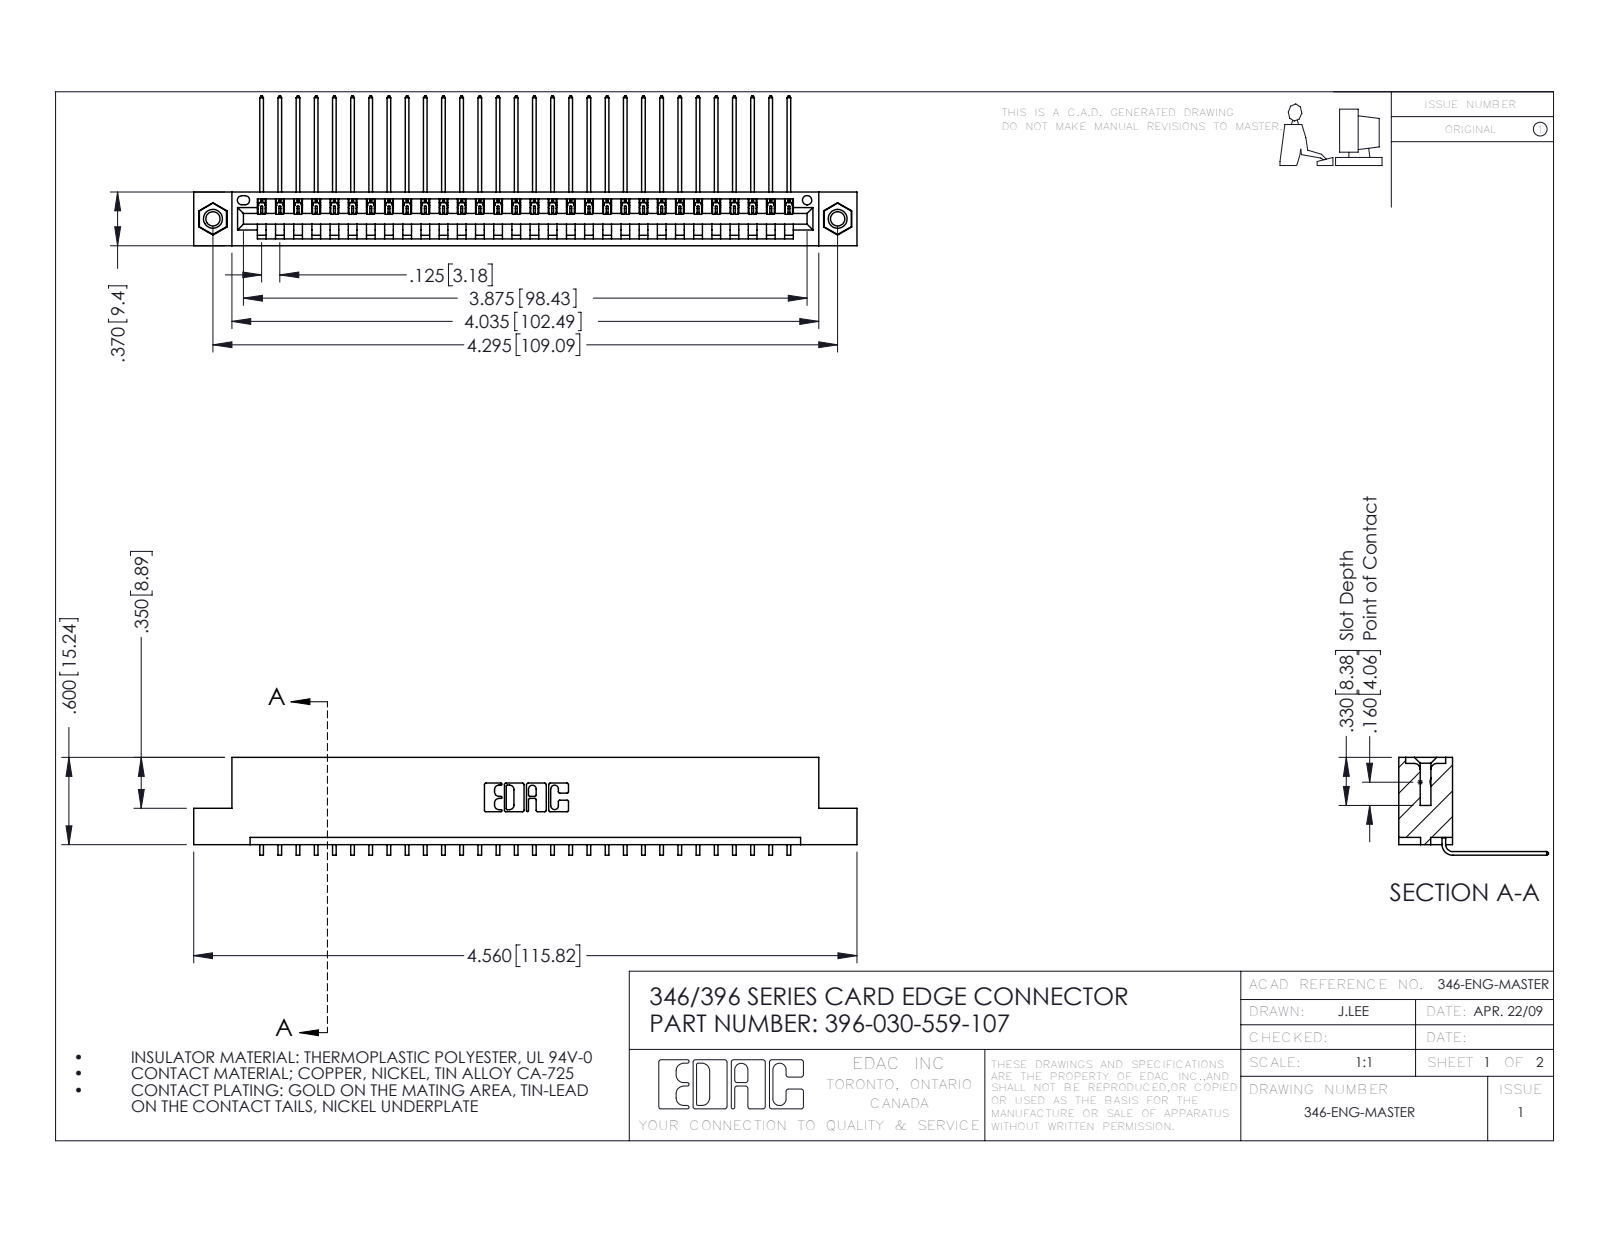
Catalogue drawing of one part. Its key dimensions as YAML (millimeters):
part_name: "396-030-559-107; 346 Part_Flush Mounting Lugs - 0.156 Dia-TI; 345-250-001_345-250-005-103; 345-292-001_558 559 Tail - 1"
step_written_by: "SolidWorks 2016 (CONFIG_CONTROL_DESIGN)"
units: millimeters
bodies: {solids: 33, faces: 1982, planar: 1368, cylindrical: 598, other: 16}
overall_size: [115.8, 26.2, 17.1]
volume: 11100
surface_area: 14360
round_holes:
  - {diameter: 2.5, count: 2}
  - {diameter: 3.2, count: 2}
  - {diameter: 4, count: 2}
  - {diameter: 1.6, count: 1}
round_bosses_or_shafts:
  - {diameter: 3.9, count: 2}
partial_cylinders:
  - {radius: 0.2, count: 60}
  - {radius: 0.3, count: 22}
  - {radius: 0.2, count: 6}
  - {radius: 0.8, count: 6}
  - {radius: 0.7, count: 3}
  - {radius: 0.8, count: 2}
  - {radius: 1, count: 2}
  - {radius: 0.4, count: 1}
face_to_face_distances: [1.2, 8.2, 9.4, 6.4, 1.8, 0.6, 7.6, 3.8, 5.6, 2.5]
hole_center_spacings: [6.2, 103.8, 109.1]
